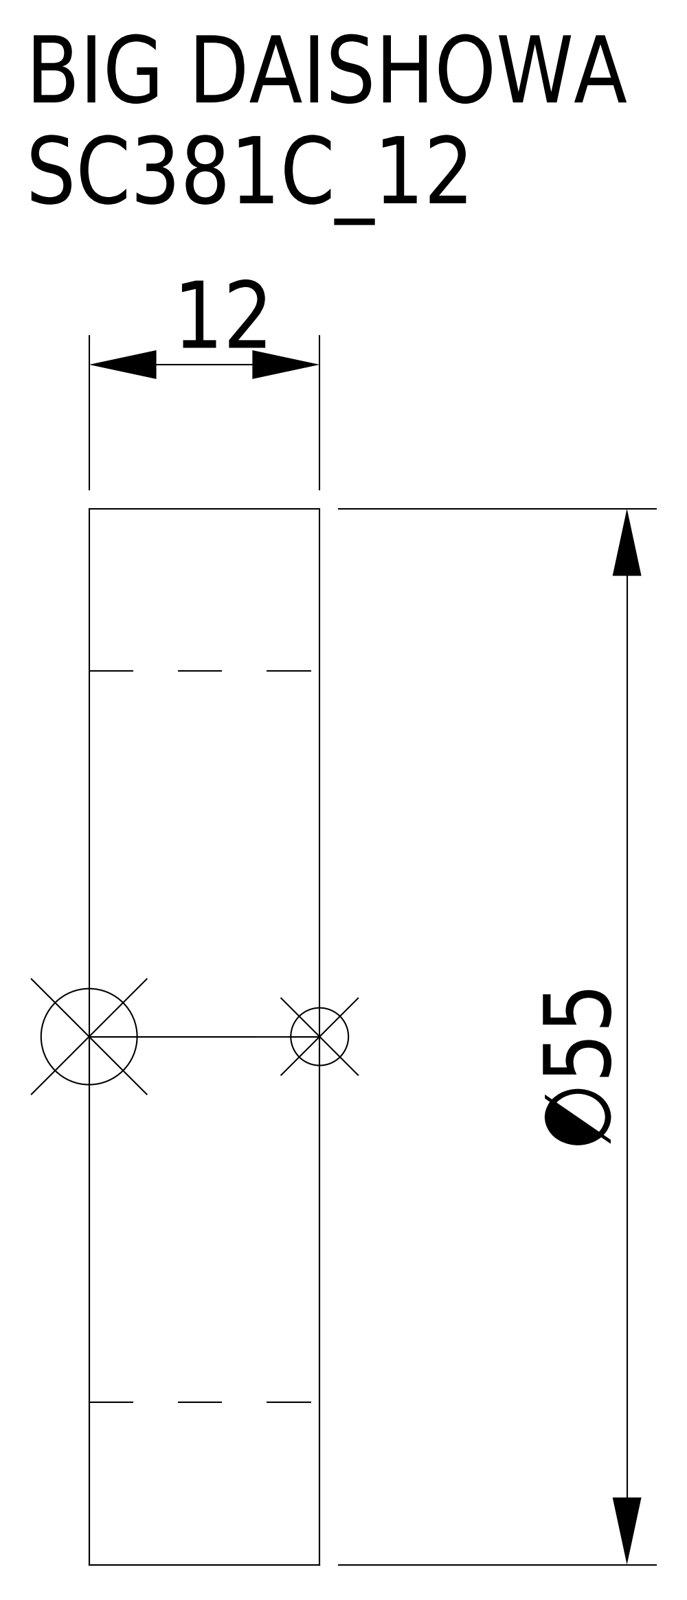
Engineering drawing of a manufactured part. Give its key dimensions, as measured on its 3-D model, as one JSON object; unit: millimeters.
{"part_name": "SC381C_12", "step_written_by": "CREO PARAMETRIC BY PTC INC, 2016380 (AUTOMOTIVE_DESIGN)", "units": "millimeters", "bodies": {"solids": 1, "faces": 8, "planar": 5, "cylindrical": 3, "other": 0}, "overall_size": [55, 55, 12], "volume_mm3": 14310, "surface_area_mm2": 6010, "round_holes": [[38.1, 1]], "round_bosses_or_shafts": [[55, 1]], "face_to_face_distances": [12, 9.8]}
